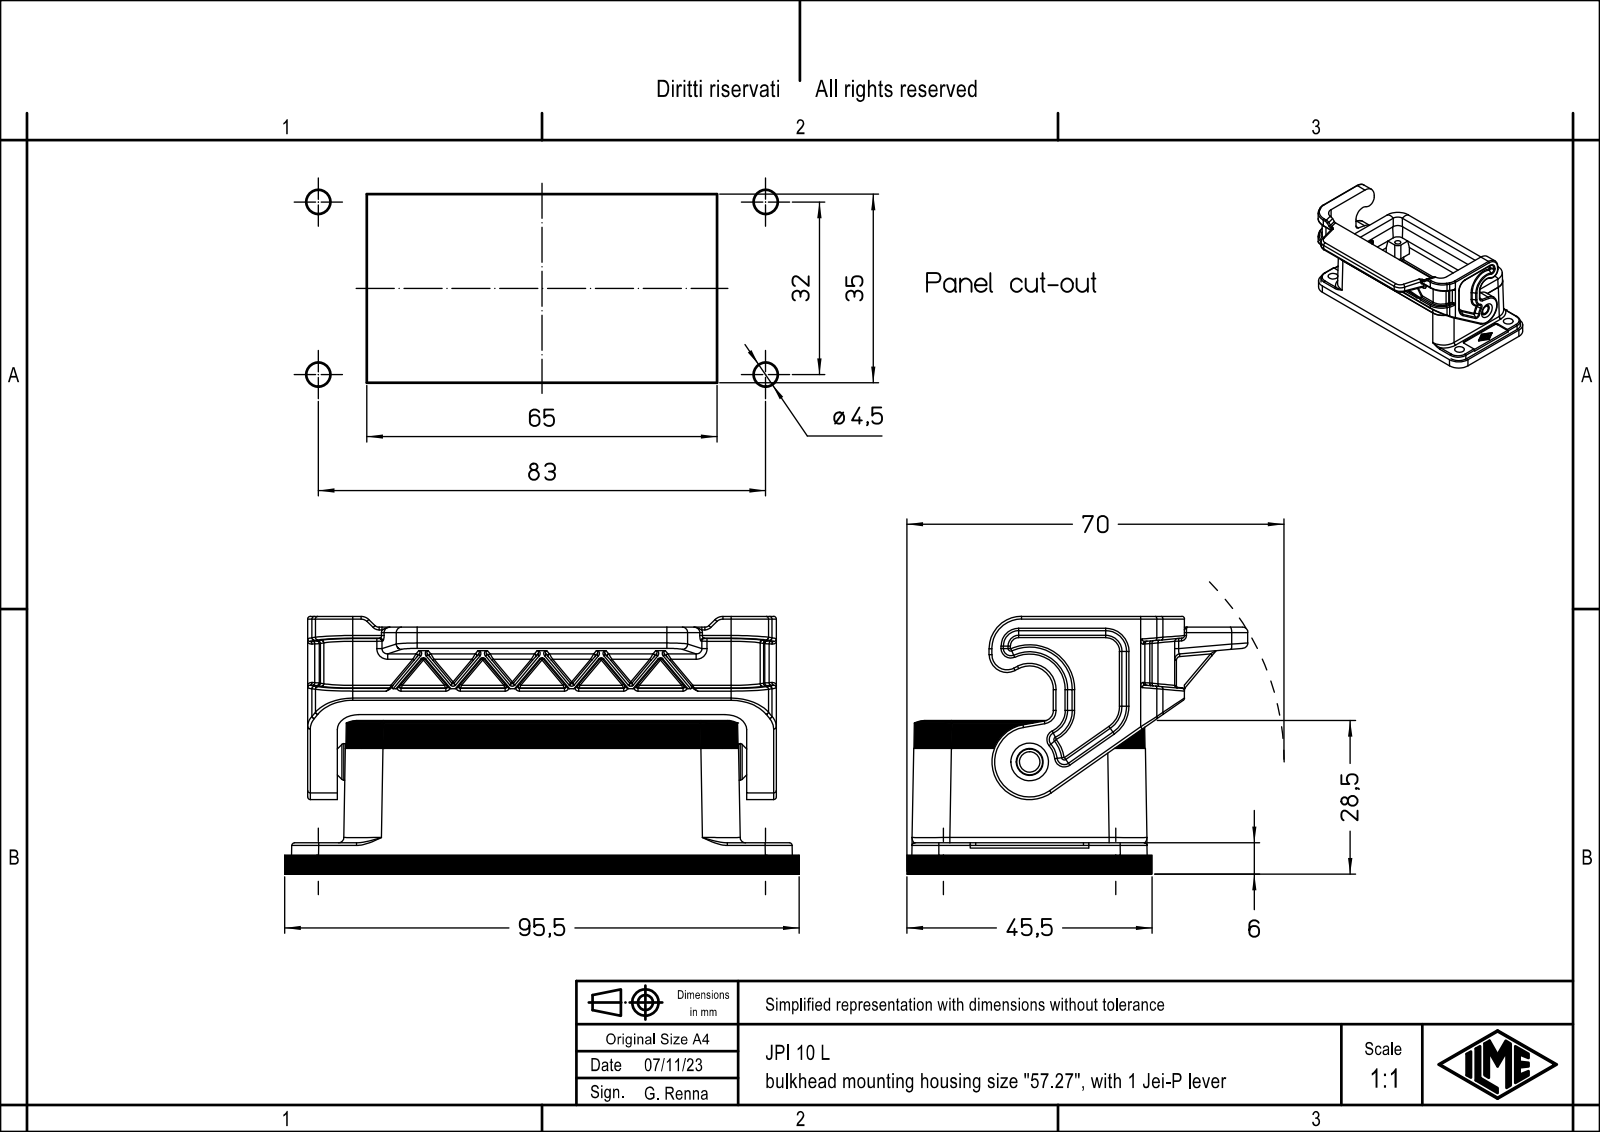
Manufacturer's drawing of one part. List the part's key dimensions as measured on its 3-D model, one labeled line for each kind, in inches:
Part name (STEP PRODUCT): JPI 10 L
STEP written by: Creo Elements/Direct Modeling 20.1B 02-Apr-2019 (C) Parametric Technology GmbH (AUTOMOTIVE_DESIGN)
Units: inches
Bodies: 1 solid, 762 faces (225 planar, 287 cylindrical, 250 other)
Overall size (bounding box): 3.76 × 2.49 × 1.882
Volume: 2.595 in³ · Surface area: 43.11 in²
Round holes (diameter × count): ⌀0.15 ×4, ⌀0.177 ×4, ⌀0.189 ×1
Round bosses / shafts (diameter × count): ⌀0.268 ×1
Partial cylindrical surfaces — rounded edges, fillets, slot ends (radius × count): R0.012 ×71, R0.02 ×63, R0.157 ×16, R0.007 ×15, R0.039 ×15, R0.079 ×9, R0.276 ×9, R0.118 ×8
Main face-to-face distances: 0.119, 0.138, 0.079, 1.803, 1.594, 0.039, 2.992, 3.209, 0.117, 1.534
Hole centre spacings: 1.26, 3.268, 3.502
